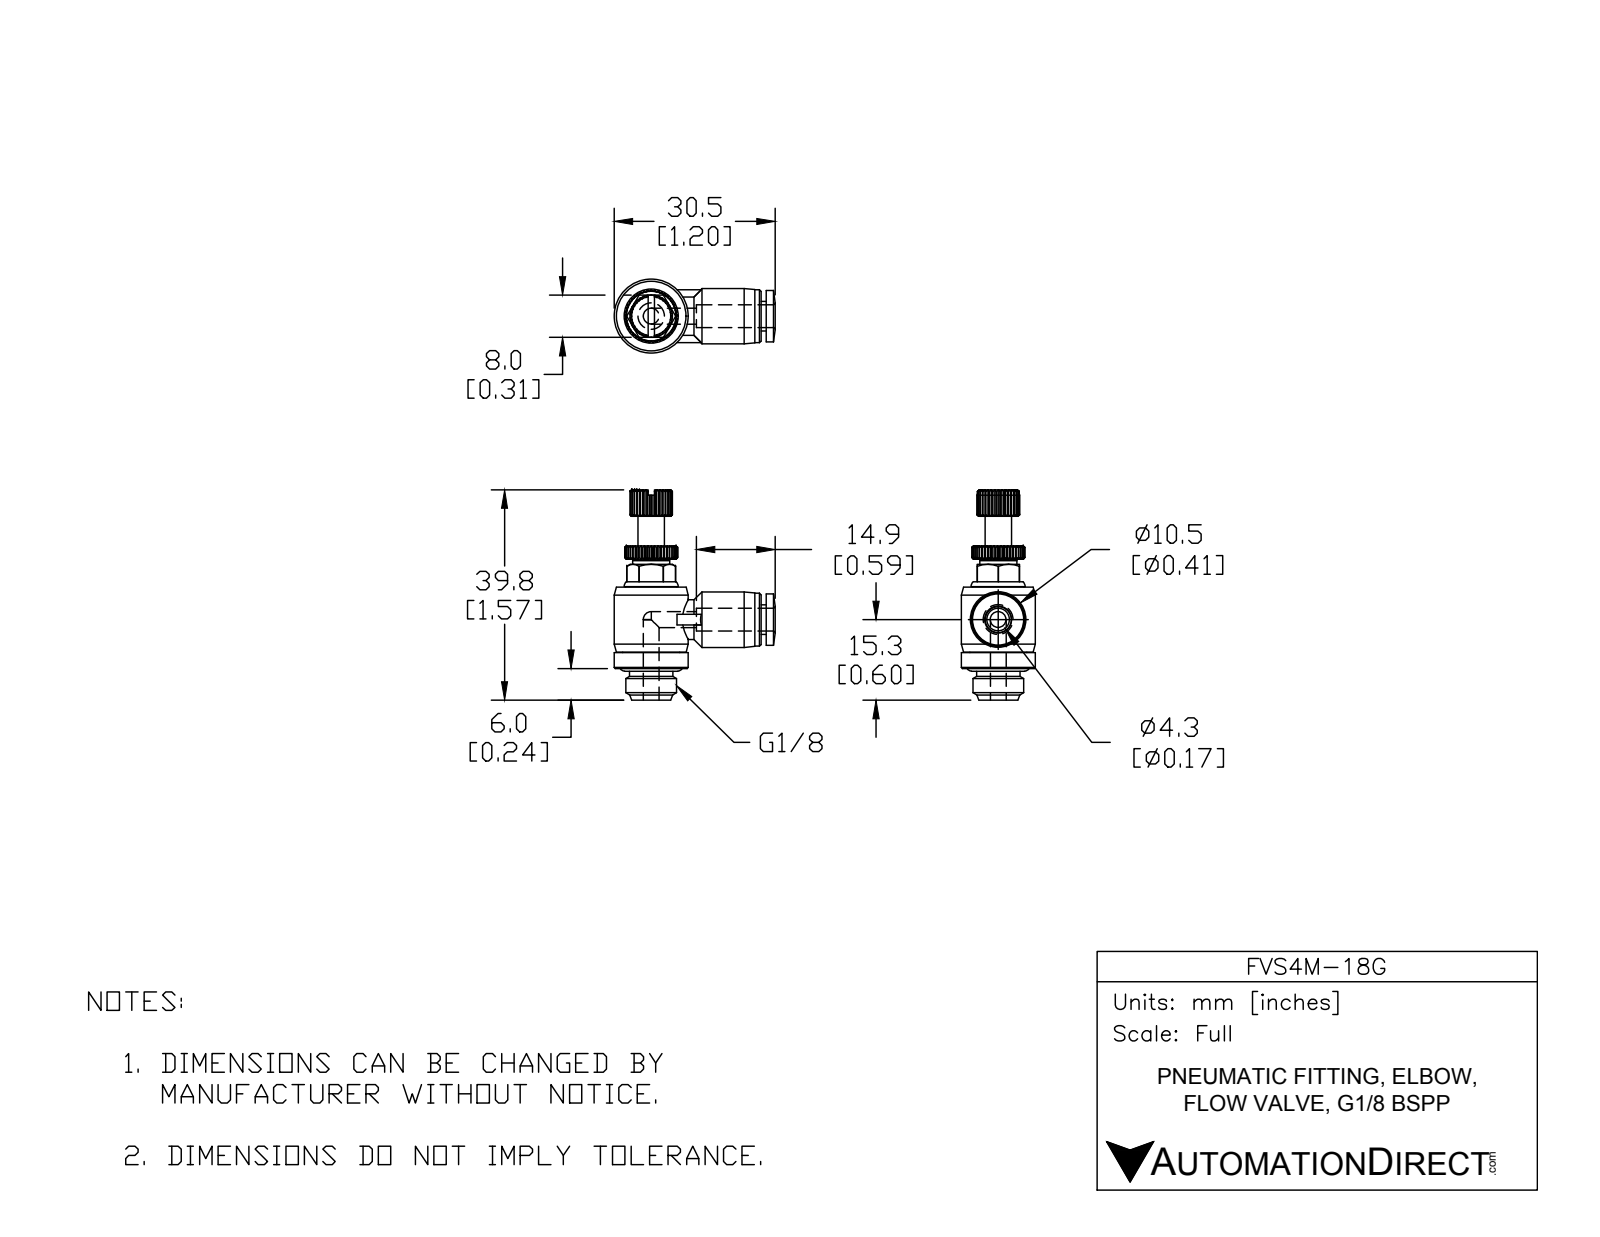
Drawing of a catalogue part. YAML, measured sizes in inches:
part_name: "FVS4M-18G"
step_written_by: "SolidWorks 2015 (AUTOMOTIVE_DESIGN)"
units: inches
bodies: {solids: 2, faces: 511, planar: 192, cylindrical: 121, other: 198}
overall_size: [1.567, 1.199, 0.551]
volume: 0.269
surface_area: 4.991
round_holes:
  - {diameter: 0.118, count: 2}
  - {diameter: 0.169, count: 1}
round_bosses_or_shafts:
  - {diameter: 0.382, count: 2}
  - {diameter: 0.551, count: 1}
  - {diameter: 0.425, count: 1}
  - {diameter: 0.413, count: 1}
  - {diameter: 0.394, count: 1}
  - {diameter: 0.378, count: 1}
  - {diameter: 0.323, count: 1}
  - {diameter: 0.295, count: 1}
partial_cylinders:
  - {radius: 0.157, count: 1}
  - {radius: 0.181, count: 1}
  - {radius: 0.197, count: 1}
face_to_face_distances: [0.488, 0.795, 0.206, 0.354, 0.039, 0.307, 0.358, 0.067, 0.063, 0.551]
